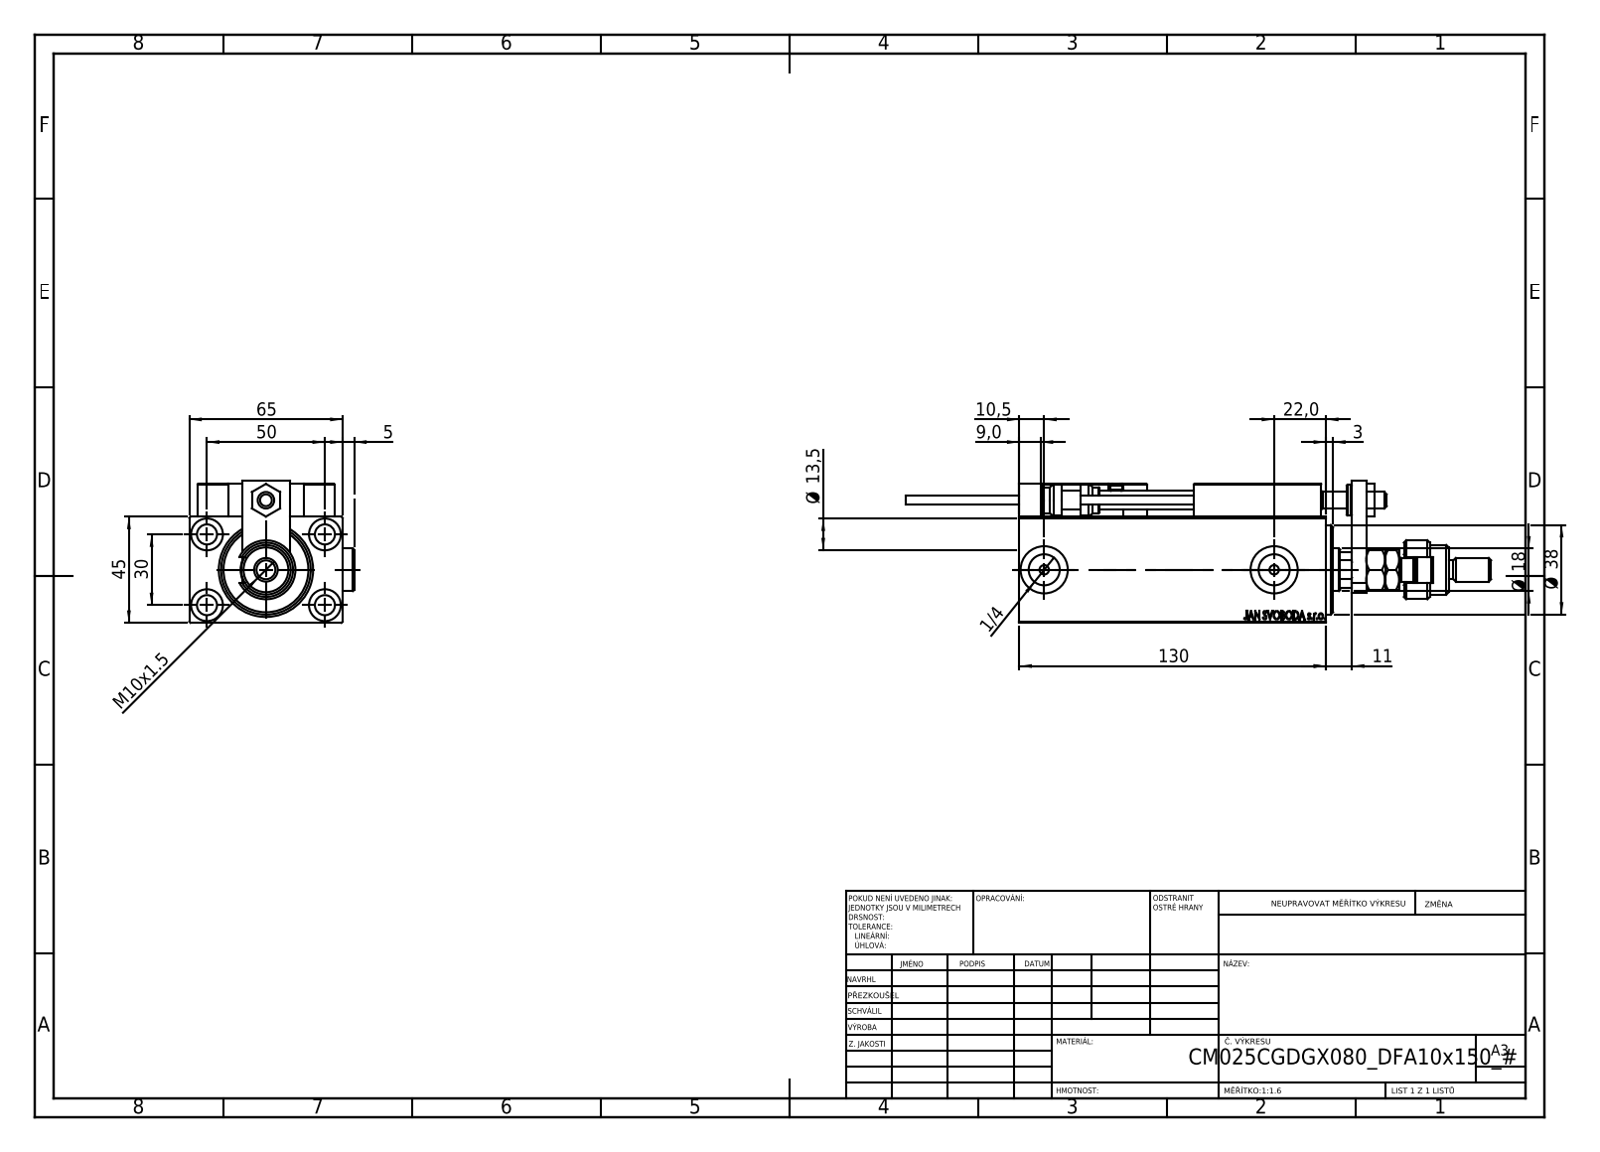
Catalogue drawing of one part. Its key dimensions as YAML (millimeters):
part_name: "V450CM_C_Body; SWITCH X; ZARAZKA; SWITCH_X_FRONT_BACK (+8 more)"
step_written_by: "SolidWorks 2019 (CONFIG_CONTROL_DESIGN)"
units: millimeters
bodies: {solids: 27, faces: 1421, planar: 622, cylindrical: 217, other: 582}
overall_size: [248, 69.9, 60.5]
volume: 384113
surface_area: 106672
round_holes:
  - {diameter: 4, count: 6}
  - {diameter: 8, count: 5}
  - {diameter: 8.5, count: 5}
  - {diameter: 3.2, count: 4}
  - {diameter: 13.5, count: 4}
  - {diameter: 5, count: 2}
  - {diameter: 13.16, count: 2}
  - {diameter: 20, count: 2}
  - {diameter: 7, count: 1}
  - {diameter: 14.5, count: 1}
  - {diameter: 18, count: 1}
  - {diameter: 21.5, count: 1}
round_bosses_or_shafts:
  - {diameter: 18, count: 2}
  - {diameter: 5, count: 2}
  - {diameter: 3.8, count: 2}
  - {diameter: 25, count: 1}
  - {diameter: 21, count: 1}
  - {diameter: 16, count: 1}
  - {diameter: 13, count: 1}
  - {diameter: 11, count: 1}
partial_cylinders:
  - {radius: 0.3, count: 30}
  - {radius: 3, count: 2}
  - {radius: 5.5, count: 1}
  - {radius: 8.5, count: 1}
  - {radius: 8.75, count: 1}
face_to_face_distances: [45, 65, 14, 6, 59, 3, 5, 13, 7, 141]
hole_center_spacings: [29.15, 11.37, 20, 28.9, 29.59, 29.69, 30, 36.06]
